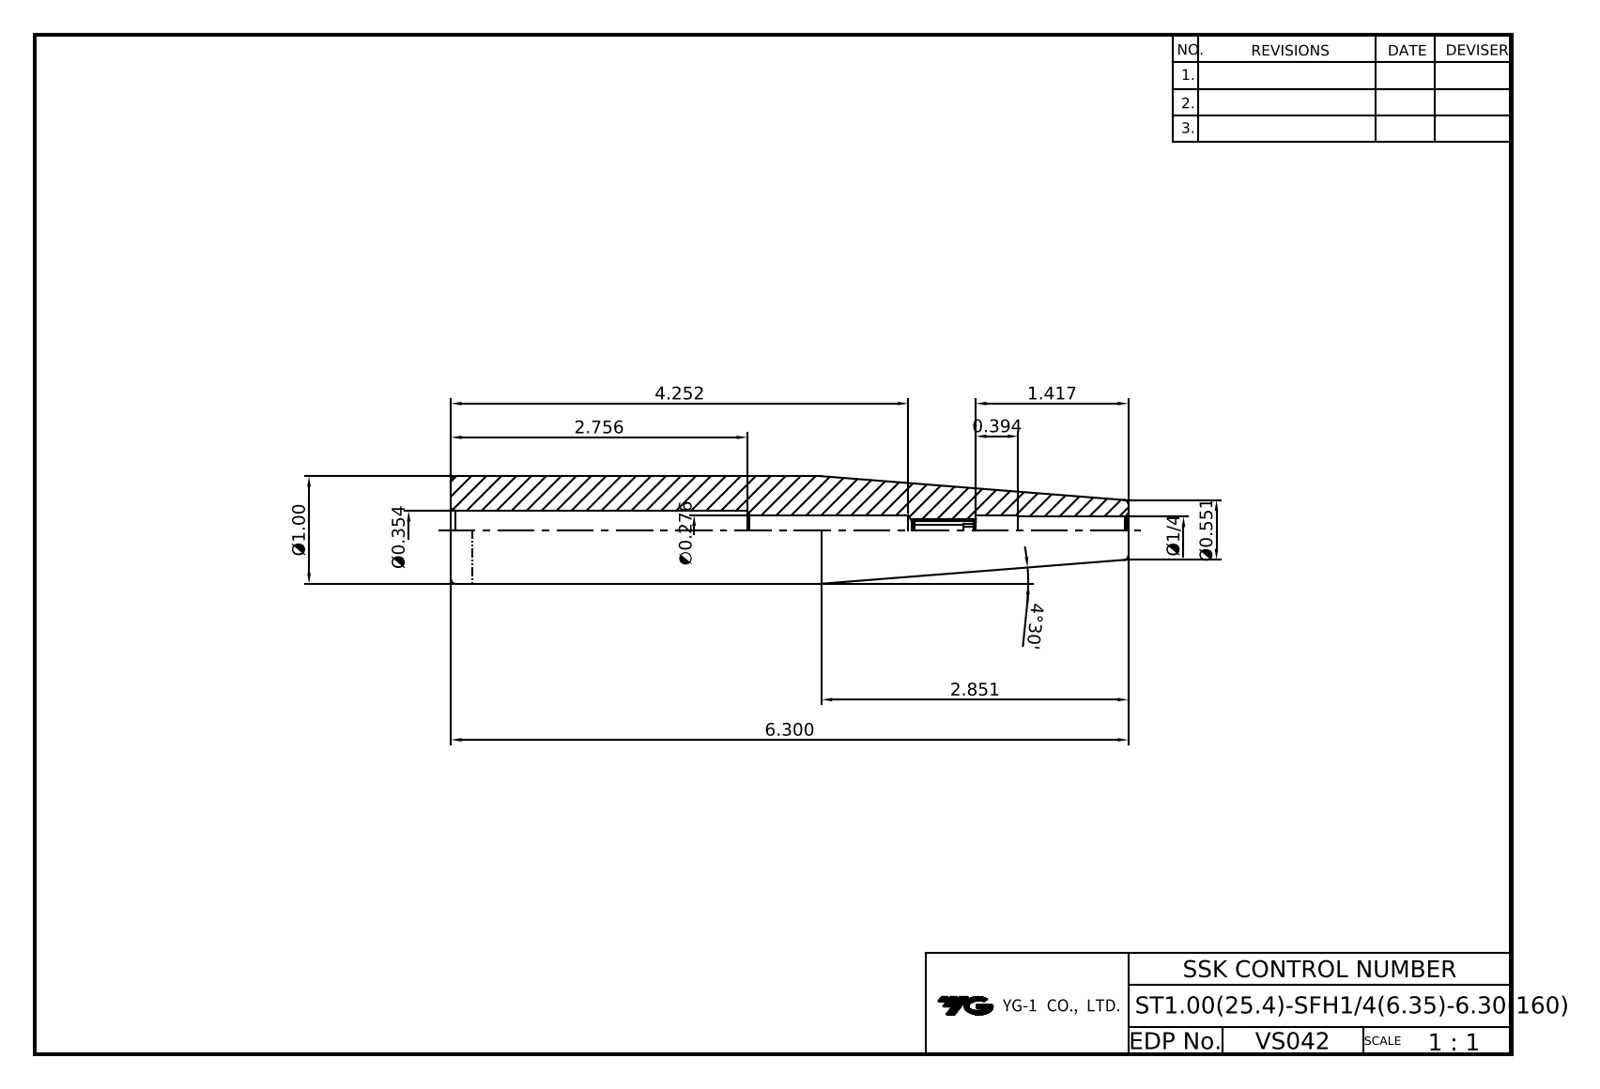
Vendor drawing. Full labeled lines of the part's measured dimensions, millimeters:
Part name (STEP PRODUCT): LO-ST25.4-SFH6.35-160
STEP written by: Autodesk Inventor 2024 (AUTOMOTIVE_DESIGN)
Units: millimetres
Bodies: 1 solid, 15 faces (4 planar, 6 cylindrical, 5 other)
Overall size (bounding box): 160 × 25.4 × 25.4
Volume: 59 647 mm³ · Surface area: 15 845 mm²
Round holes (diameter × count): ⌀4.13 ×1, ⌀6.35 ×1, ⌀7 ×1, ⌀7.35 ×1, ⌀9 ×1
Round bosses / shafts (diameter × count): ⌀25.4 ×1
Main face-to-face distances: 160, 124, 36, 134, 10, 26
